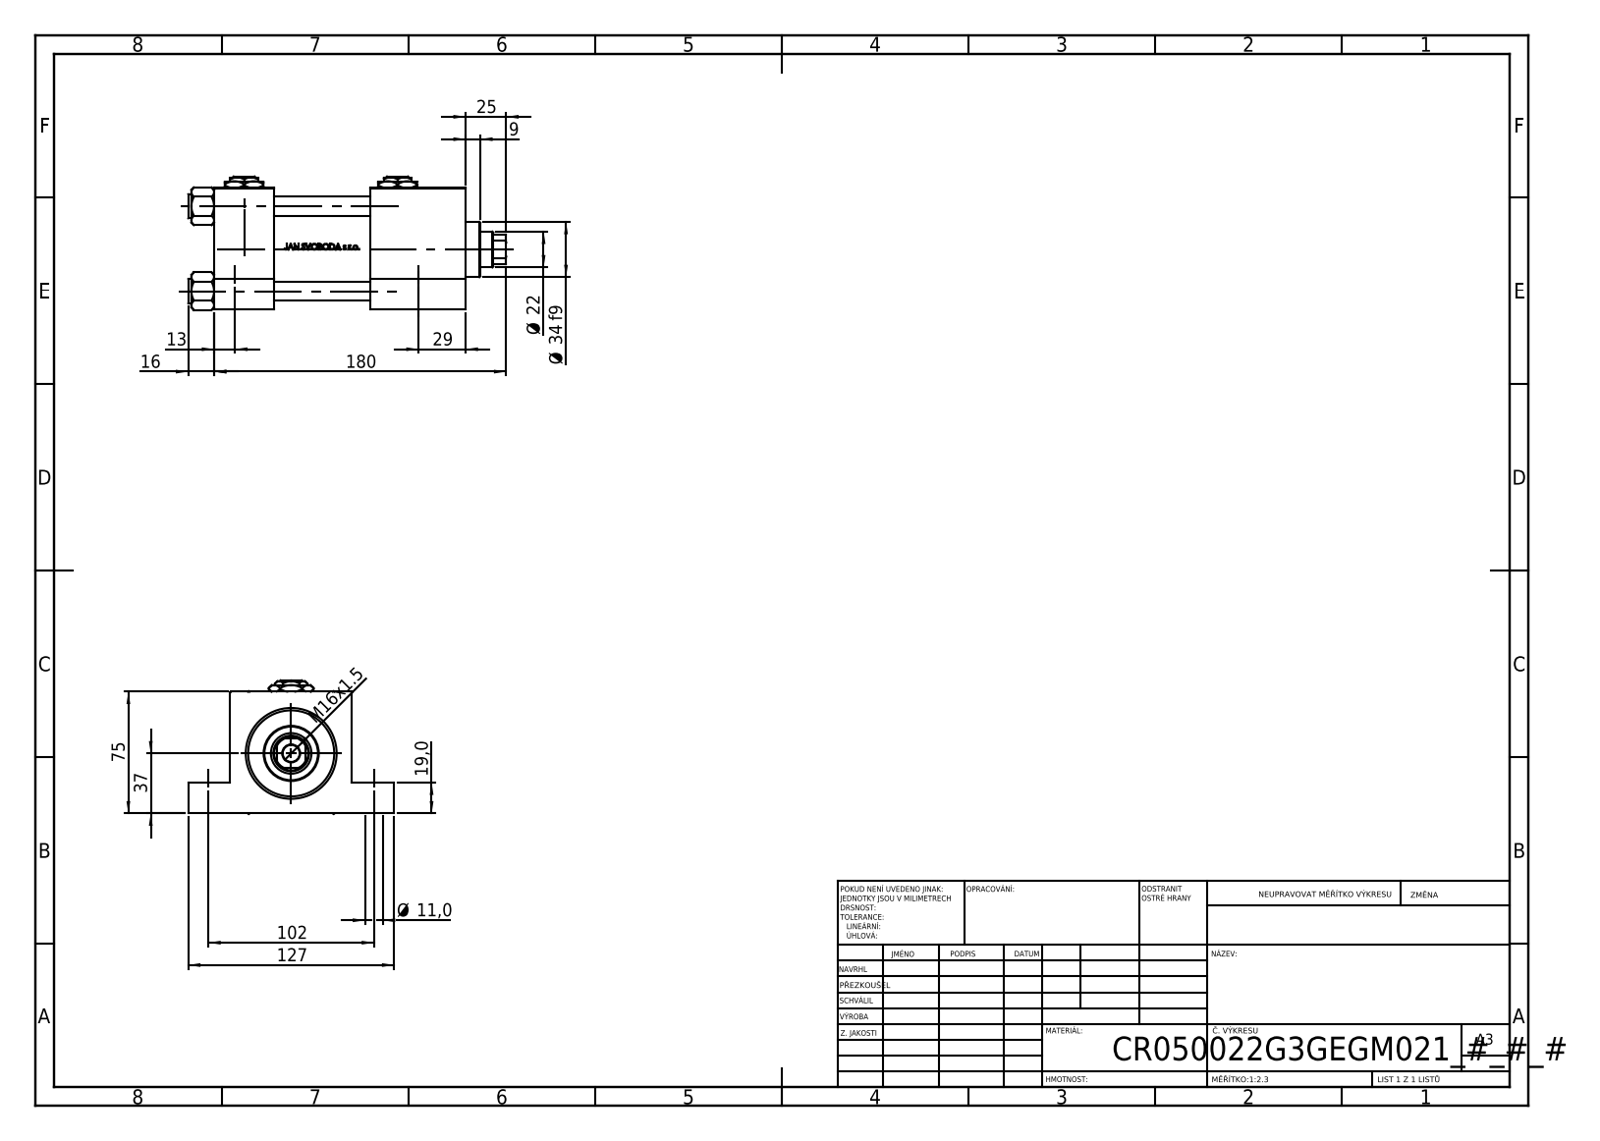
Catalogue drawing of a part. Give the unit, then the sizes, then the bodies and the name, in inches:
Units: inches
Overall size (bounding box): 7.717 × 5 × 3.239
Round holes (diameter × count): ⌀0.433 ×4, ⌀0.472 ×4, ⌀0.276 ×2, ⌀0.825 ×2, ⌀1.181 ×2, ⌀0.413 ×1, ⌀0.866 ×1, ⌀0.984 ×1, ⌀1.614 ×1, ⌀1.969 ×1, ⌀2.087 ×1
Round bosses / shafts (diameter × count): ⌀0.591 ×4, ⌀2.205 ×1, ⌀1.339 ×1
Partial cylindrical surfaces — rounded edges, fillets, slot ends (radius × count): R0.413 ×1
Main face-to-face distances: 2.953, 2.323, 1.457, 6.102, 4.646, 0.748, 2.205, 3.78, 1.024, 3.976
Hole centre spacings: 2.059, 1.442, 1.47, 2.02, 2.072, 2.912, 4.016, 4.419
Volume: 46.53 in³ · Surface area: 252.4 in²
Bodies: 13 solids, 1172 faces (476 planar, 124 cylindrical, 572 other)
Part name (STEP PRODUCT): NUT_M5_G; V215CR_G_Body; V215CR_G_TYCINKA; V215_VC_A (+2 more)
STEP written by: SolidWorks 2019 (CONFIG_CONTROL_DESIGN)
